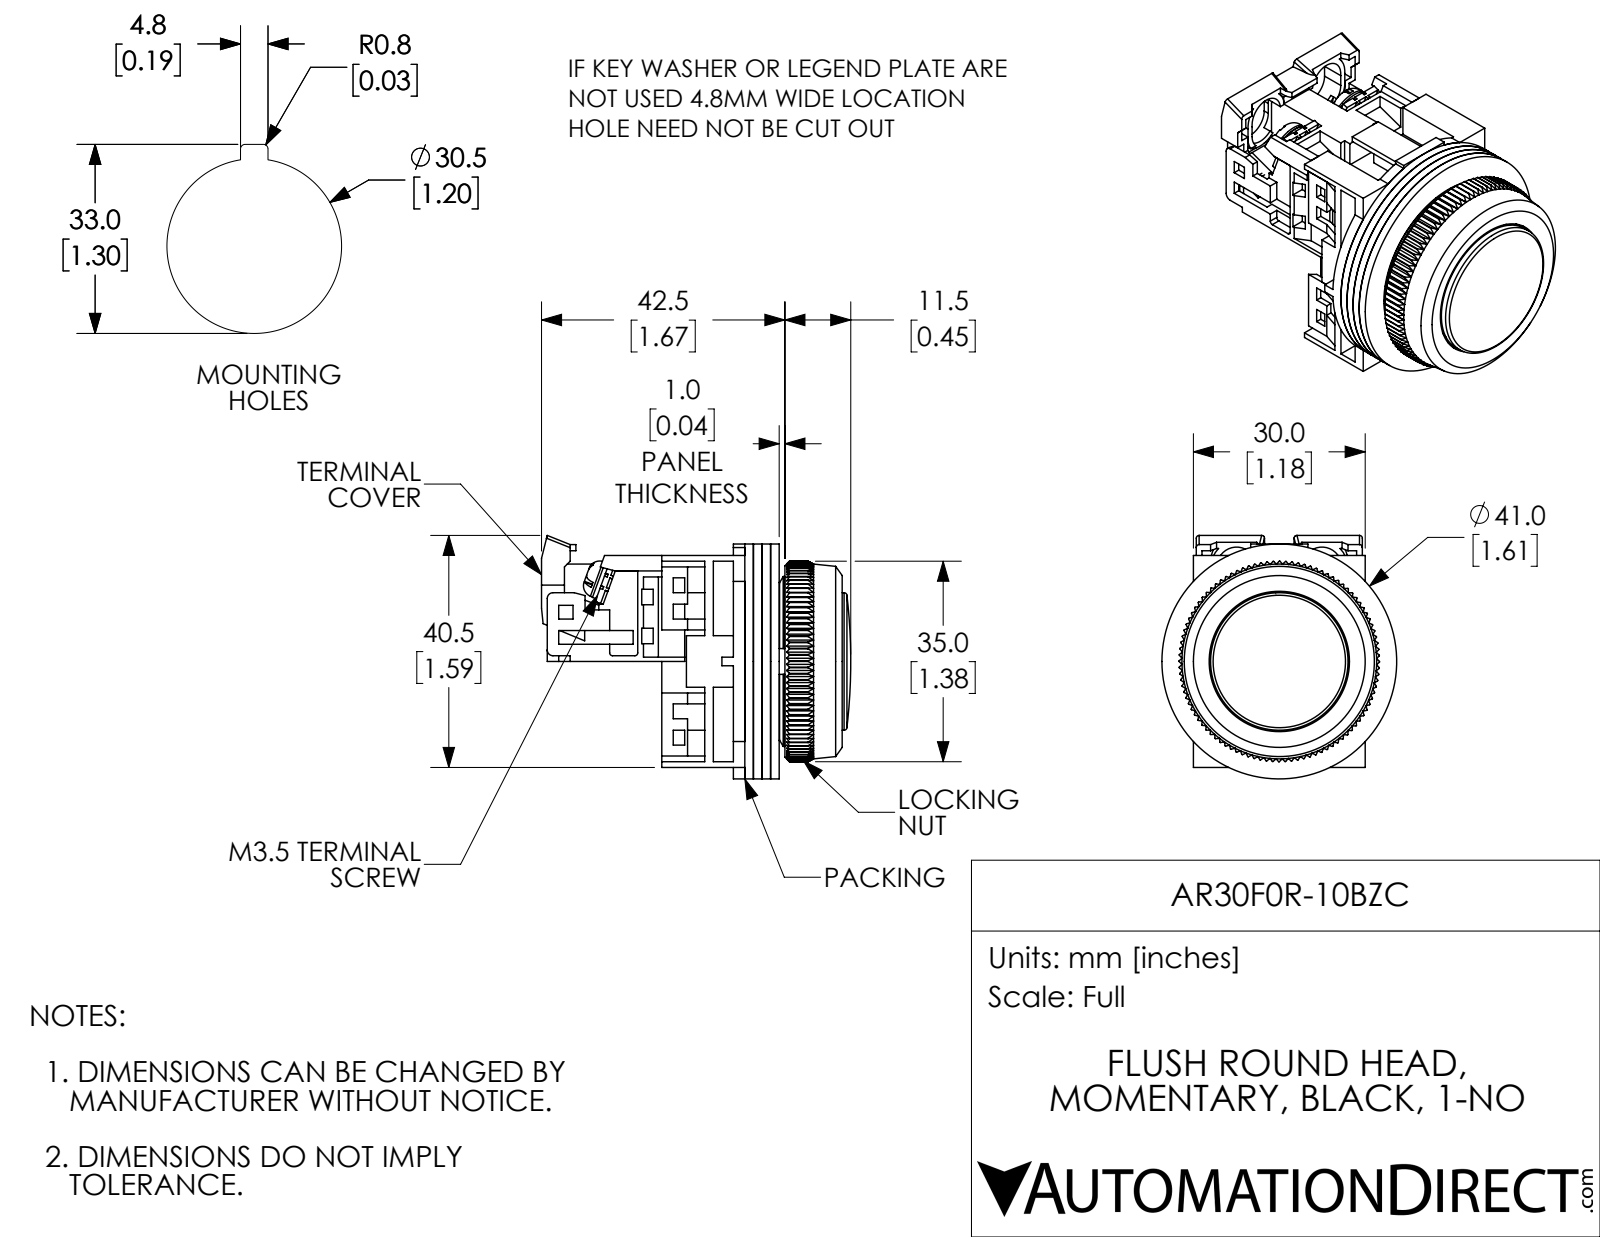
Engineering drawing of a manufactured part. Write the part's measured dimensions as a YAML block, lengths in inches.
part_name: "AR30F0R-10BZC"
step_written_by: "SolidWorks 2017 (AUTOMOTIVE_DESIGN)"
units: inches
bodies: {solids: 16, faces: 1258, planar: 798, cylindrical: 249, other: 211}
overall_size: [2.125, 1.673, 1.614]
volume: 1.595
surface_area: 47.89
round_holes:
  - {diameter: 0.138, count: 4}
  - {diameter: 0.142, count: 2}
  - {diameter: 0.118, count: 1}
  - {diameter: 0.472, count: 1}
  - {diameter: 0.709, count: 1}
  - {diameter: 0.787, count: 1}
  - {diameter: 0.827, count: 1}
  - {diameter: 0.945, count: 1}
  - {diameter: 0.965, count: 1}
  - {diameter: 1.122, count: 1}
  - {diameter: 1.252, count: 1}
round_bosses_or_shafts:
  - {diameter: 0.26, count: 2}
  - {diameter: 0.138, count: 2}
  - {diameter: 1.614, count: 1}
  - {diameter: 1.181, count: 1}
  - {diameter: 0.906, count: 1}
  - {diameter: 0.866, count: 1}
  - {diameter: 0.551, count: 1}
partial_cylinders:
  - {radius: 0.059, count: 8}
  - {radius: 0.02, count: 6}
  - {radius: 0.039, count: 2}
  - {radius: 0.138, count: 2}
  - {radius: 0.177, count: 2}
  - {radius: 0.118, count: 1}
  - {radius: 0.398, count: 1}
  - {radius: 0.449, count: 1}
face_to_face_distances: [0.059, 0.118, 0.177, 0.039, 0.197, 0.079, 0.689, 1.417, 0.256, 0.138]
hole_center_spacings: [0.579, 0.61]
